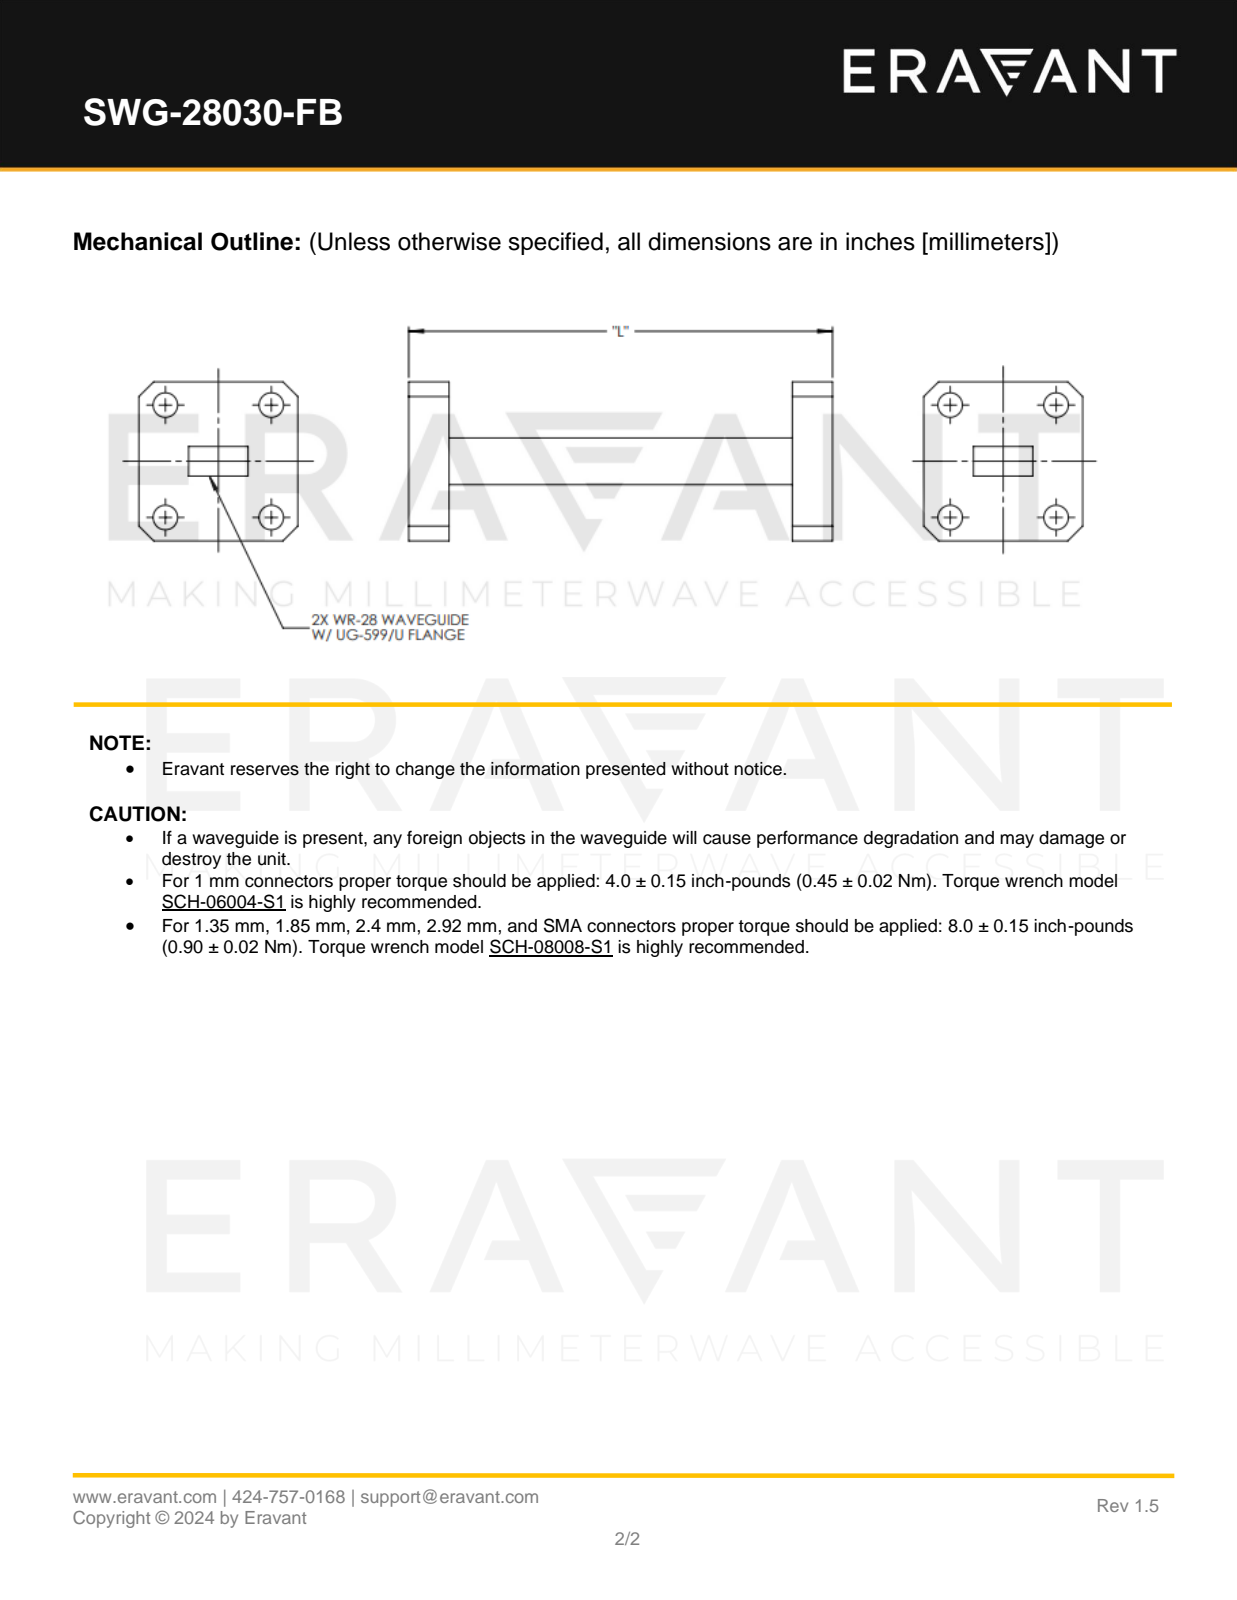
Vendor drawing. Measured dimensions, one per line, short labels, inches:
name: SWG-28030-FB
written by: SolidWorks 2021 (CONFIG_CONTROL_DESIGN)
unit: in
bodies: 1 solid, 50 faces (34 planar, 16 cylindrical, 0 other)
size: 3 × 0.75 × 0.75
volume: 0.401 in³; area: 6.571 in²
holes: 4× ⌀0.116
face distances: 0.22, 0.19, 2.81, 0.36, 3, 2.62, 0.75, 0.195, 0.555, 0.265
hole spacings: 0.5, 0.53, 0.729
